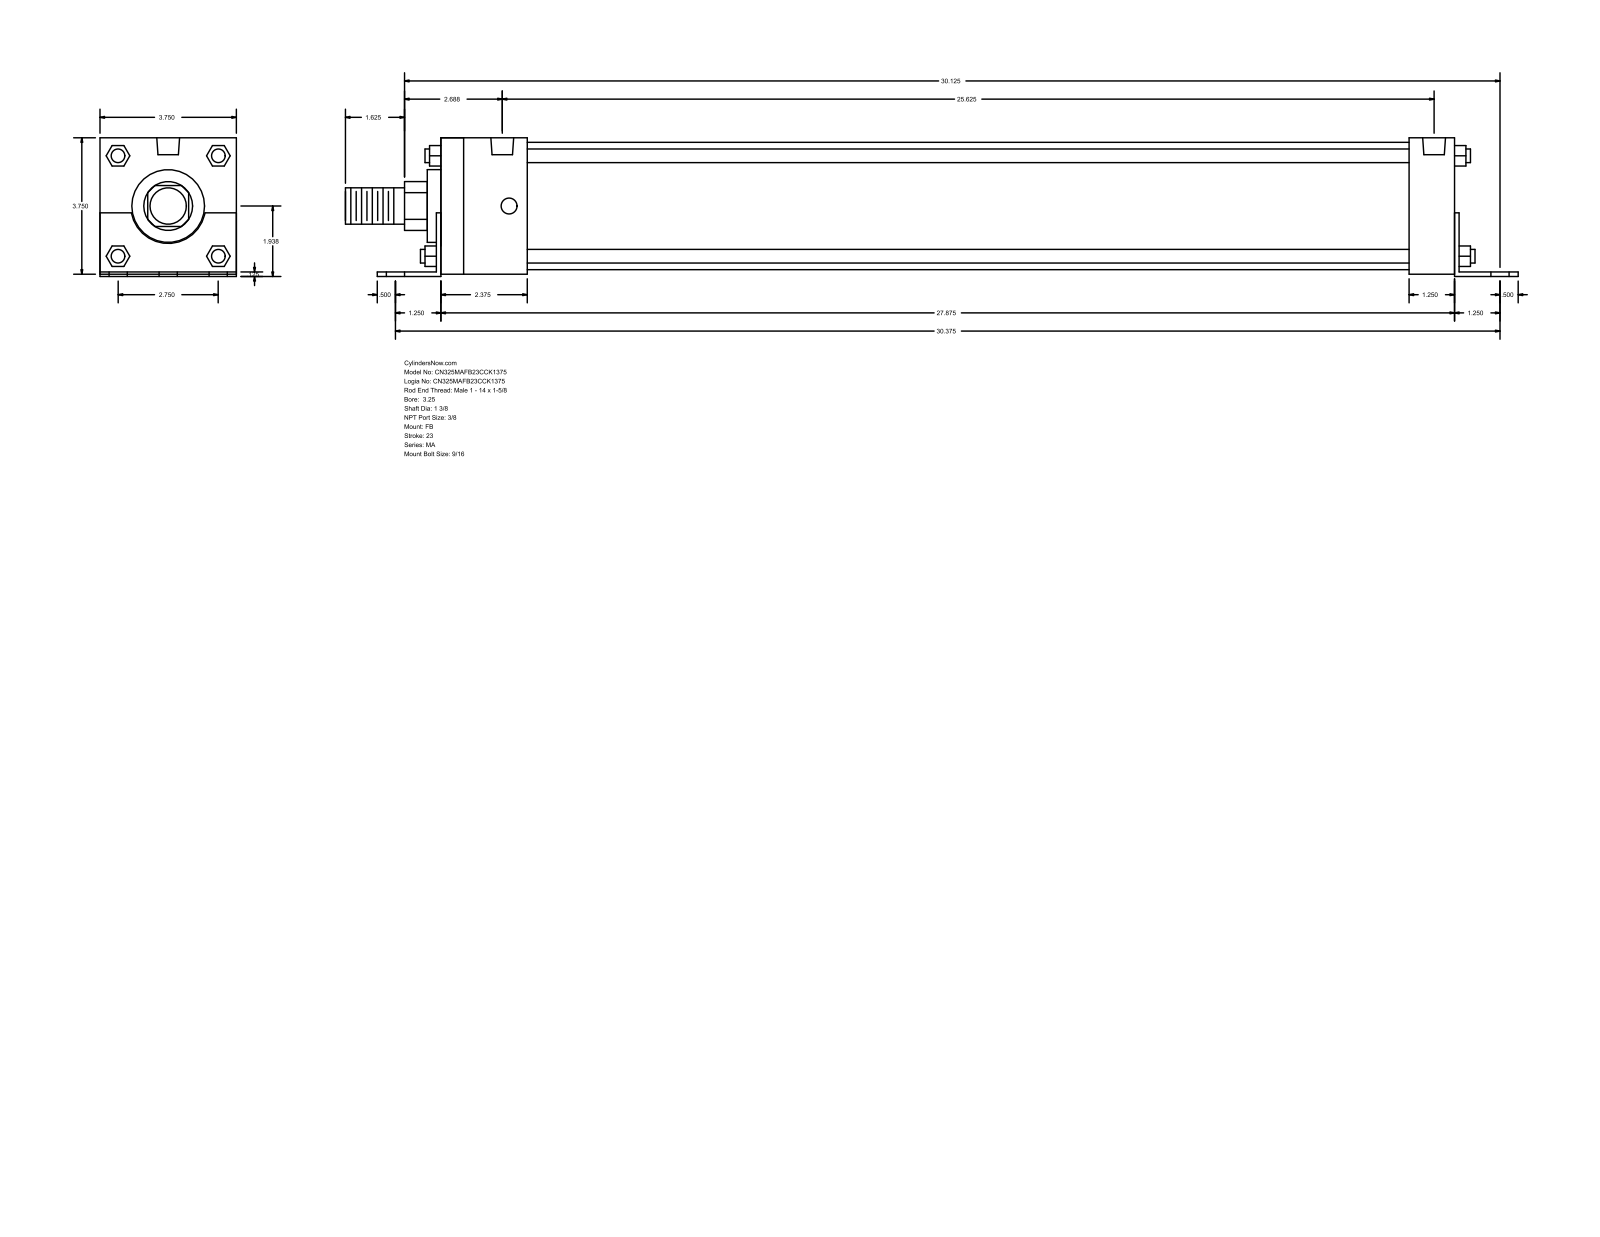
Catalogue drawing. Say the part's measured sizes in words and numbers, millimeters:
The part is named "MA_FB__0325_1.375". Its 3-D file was written by "GSSL Pune (CONFIG_CONTROL_DESIGN)". It is 0 solids with 140 faces: 105 planar, 35 cylindrical and 0 other. Overall it measures 819.15 by 96.84 by 95.25 millimeters. Round holes: 6 of diameter 14.29, 4 of diameter 11.11, 2 of diameter 15.93. Round bosses or shafts: 4 of diameter 9.53, 1 of diameter 88.9, 1 of diameter 50.8, 1 of diameter 34.92, 1 of diameter 25.4. Partial cylindrical surfaces (rounded edges, fillets, slot ends): 1 of radius 17.06, 1 of radius 26.16. The main face-to-face distances are 95.24, 3.17, 1.59, 96.83, 1.58, 93.66, 3.18, 708.02, 711.2, 31.75. The hole center spacings are 34.92, 772.31, 771.52, 57.78, 61.64, 69.84, 82.38, 86.72.
